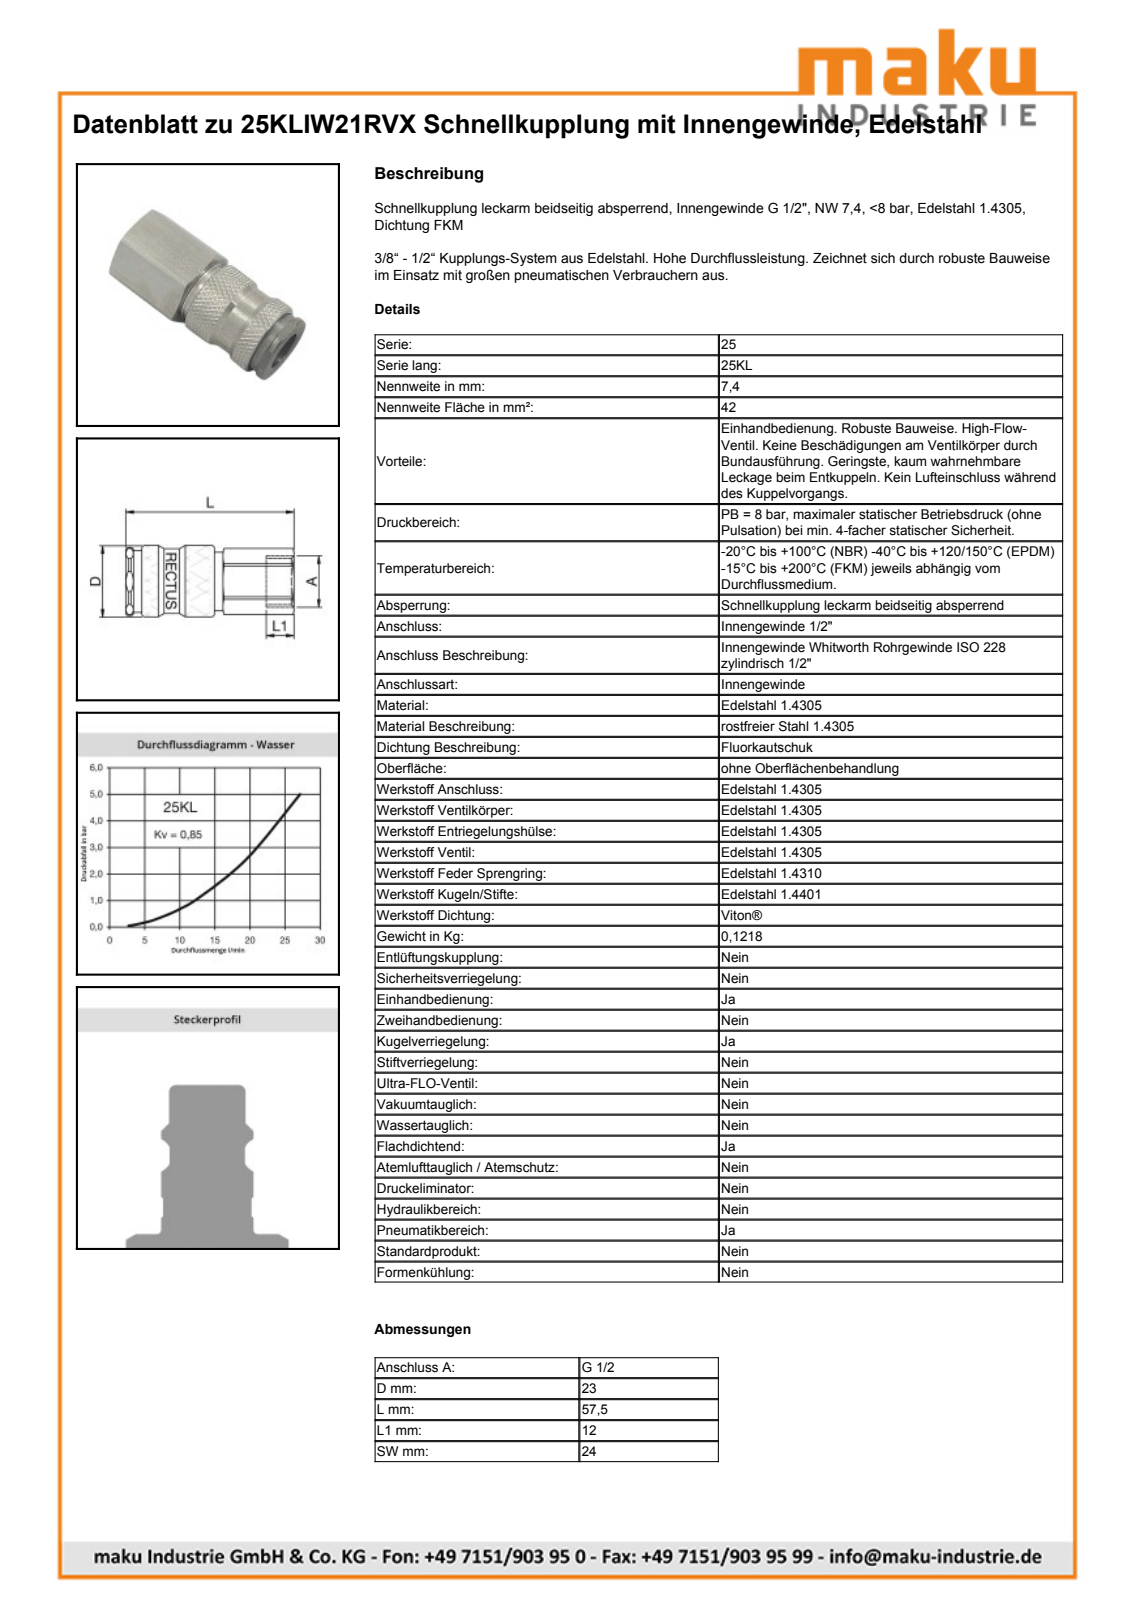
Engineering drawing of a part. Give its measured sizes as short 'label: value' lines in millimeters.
name: D110450
written by: Autodesk Inventor 2013 (AUTOMOTIVE_DESIGN)
unit: mm
bodies: 2 solids, 586 faces (237 planar, 72 cylindrical, 277 other)
size: 57.5 × 26.97 × 25.34
volume: 20 590 mm³; area: 9 193 mm²
holes: 1× ⌀17.25, 1× ⌀18.63, 1× ⌀19.35, 1× ⌀20.05
bosses: 1× ⌀23.15, 1× ⌀22, 1× ⌀21, 1× ⌀20, 1× ⌀18.95, 1× ⌀16.72
rounds: 1× R10.4, 1× R13.53
face distances: 24, 45.5, 31.45, 14.05, 57.5, 26.05, 12, 24.5, 6.95, 21
